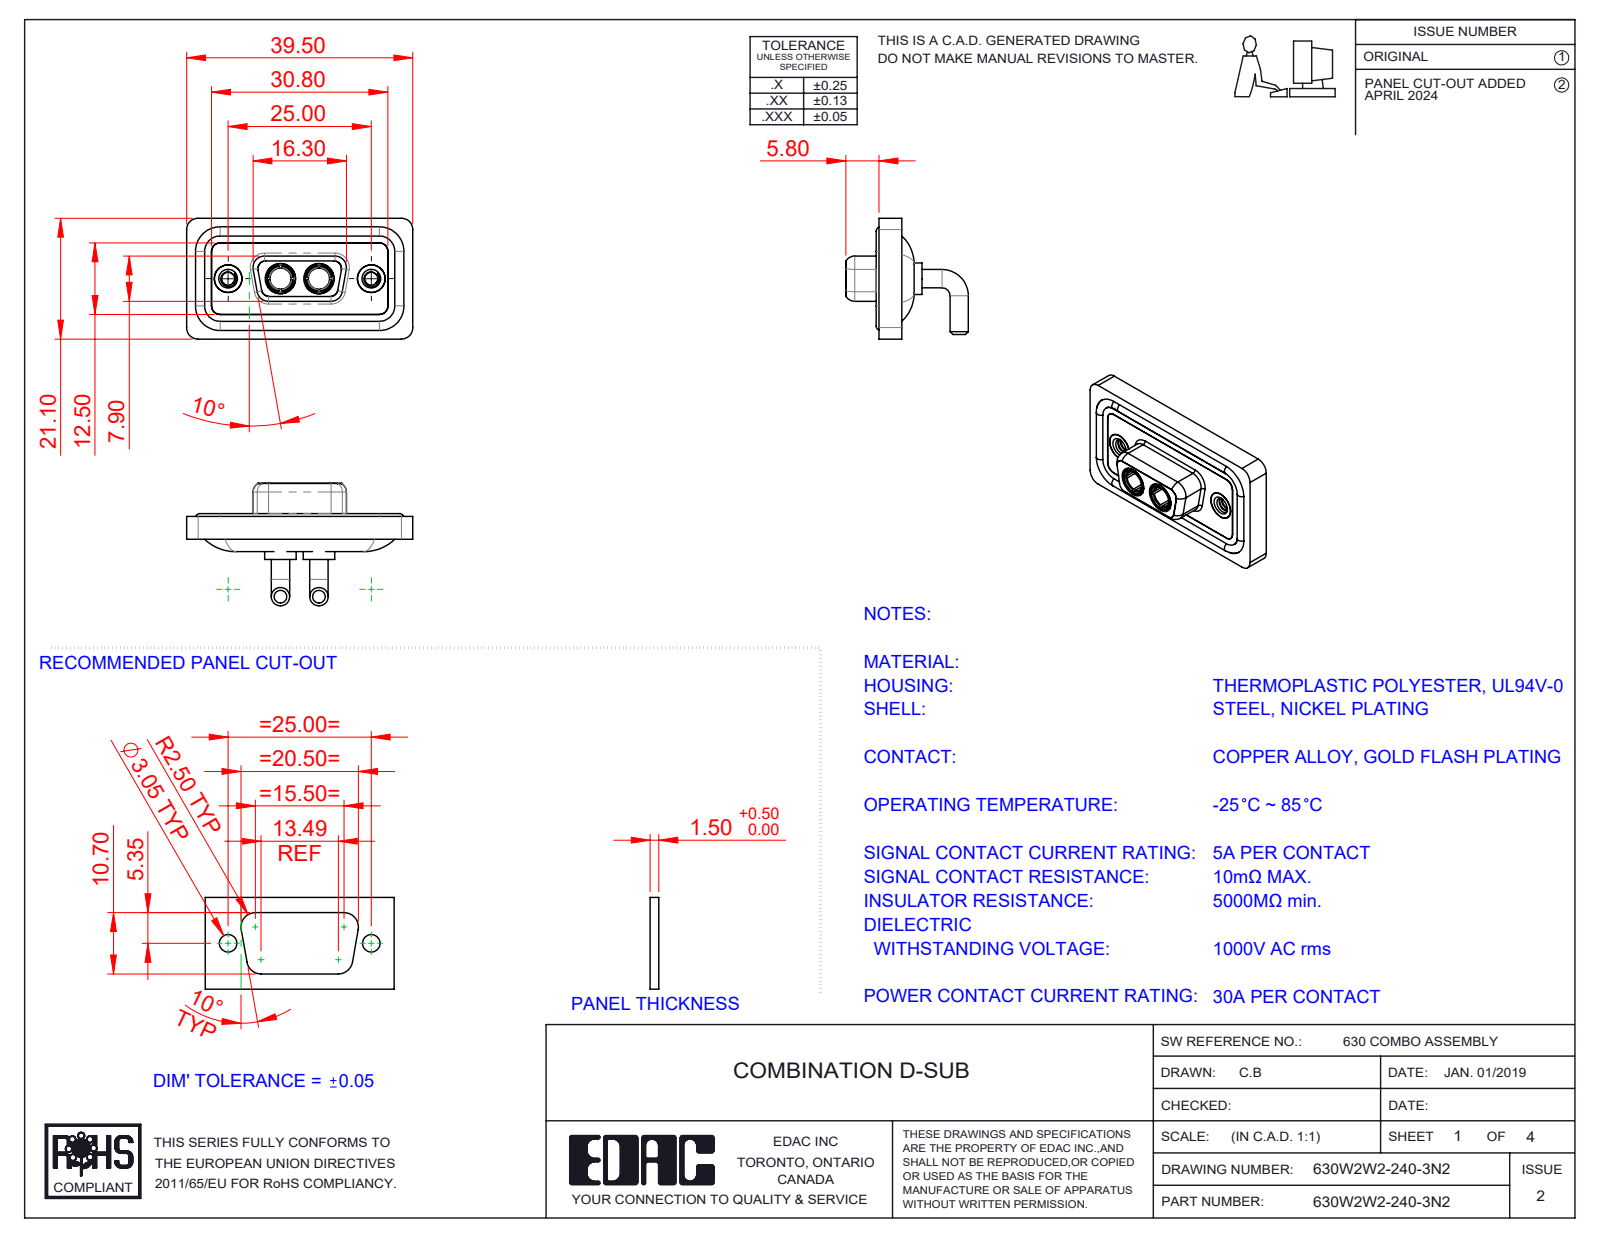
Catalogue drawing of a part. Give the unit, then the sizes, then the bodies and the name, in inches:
Units: inches
Overall size (bounding box): 1.555 × 0.843 × 0.831
Round holes (diameter × count): ⌀0.191 ×4, ⌀0.089 ×2, ⌀0.146 ×2, ⌀0.157 ×2, ⌀0.159 ×2, ⌀0.197 ×2, ⌀0.209 ×2
Round bosses / shafts (diameter × count): ⌀0.126 ×4, ⌀0.063 ×4, ⌀0.217 ×2, ⌀0.205 ×2, ⌀0.195 ×2, ⌀0.195 ×2, ⌀0.189 ×2, ⌀0.187 ×2
Partial cylindrical surfaces — rounded edges, fillets, slot ends (radius × count): R0.059 ×18, R0.079 ×18, R0.053 ×8, R0.063 ×8, R0.01 ×4, R0.02 ×4, R0.024 ×4, R0.026 ×4
Main face-to-face distances: 0.016, 0.071, 0.043, 0.114, 0.098, 0.063, 0.122, 0.059, 0.083, 0.02
Hole centre spacings: 0.36, 0.624, 0.265, 0.984
Volume: 0.297 in³ · Surface area: 12.12 in²
Bodies: 11 solids, 542 faces (163 planar, 238 cylindrical, 141 other)
Part name (STEP PRODUCT): 630Combo Housing_2W2; 630W2W2-240-3N2; 630Combo Shell Rear_09 Contacts; 630Combo Shell Front_09 Contacts (+3 more)
STEP written by: SolidWorks 2023 (CONFIG_CONTROL_DESIGN)
